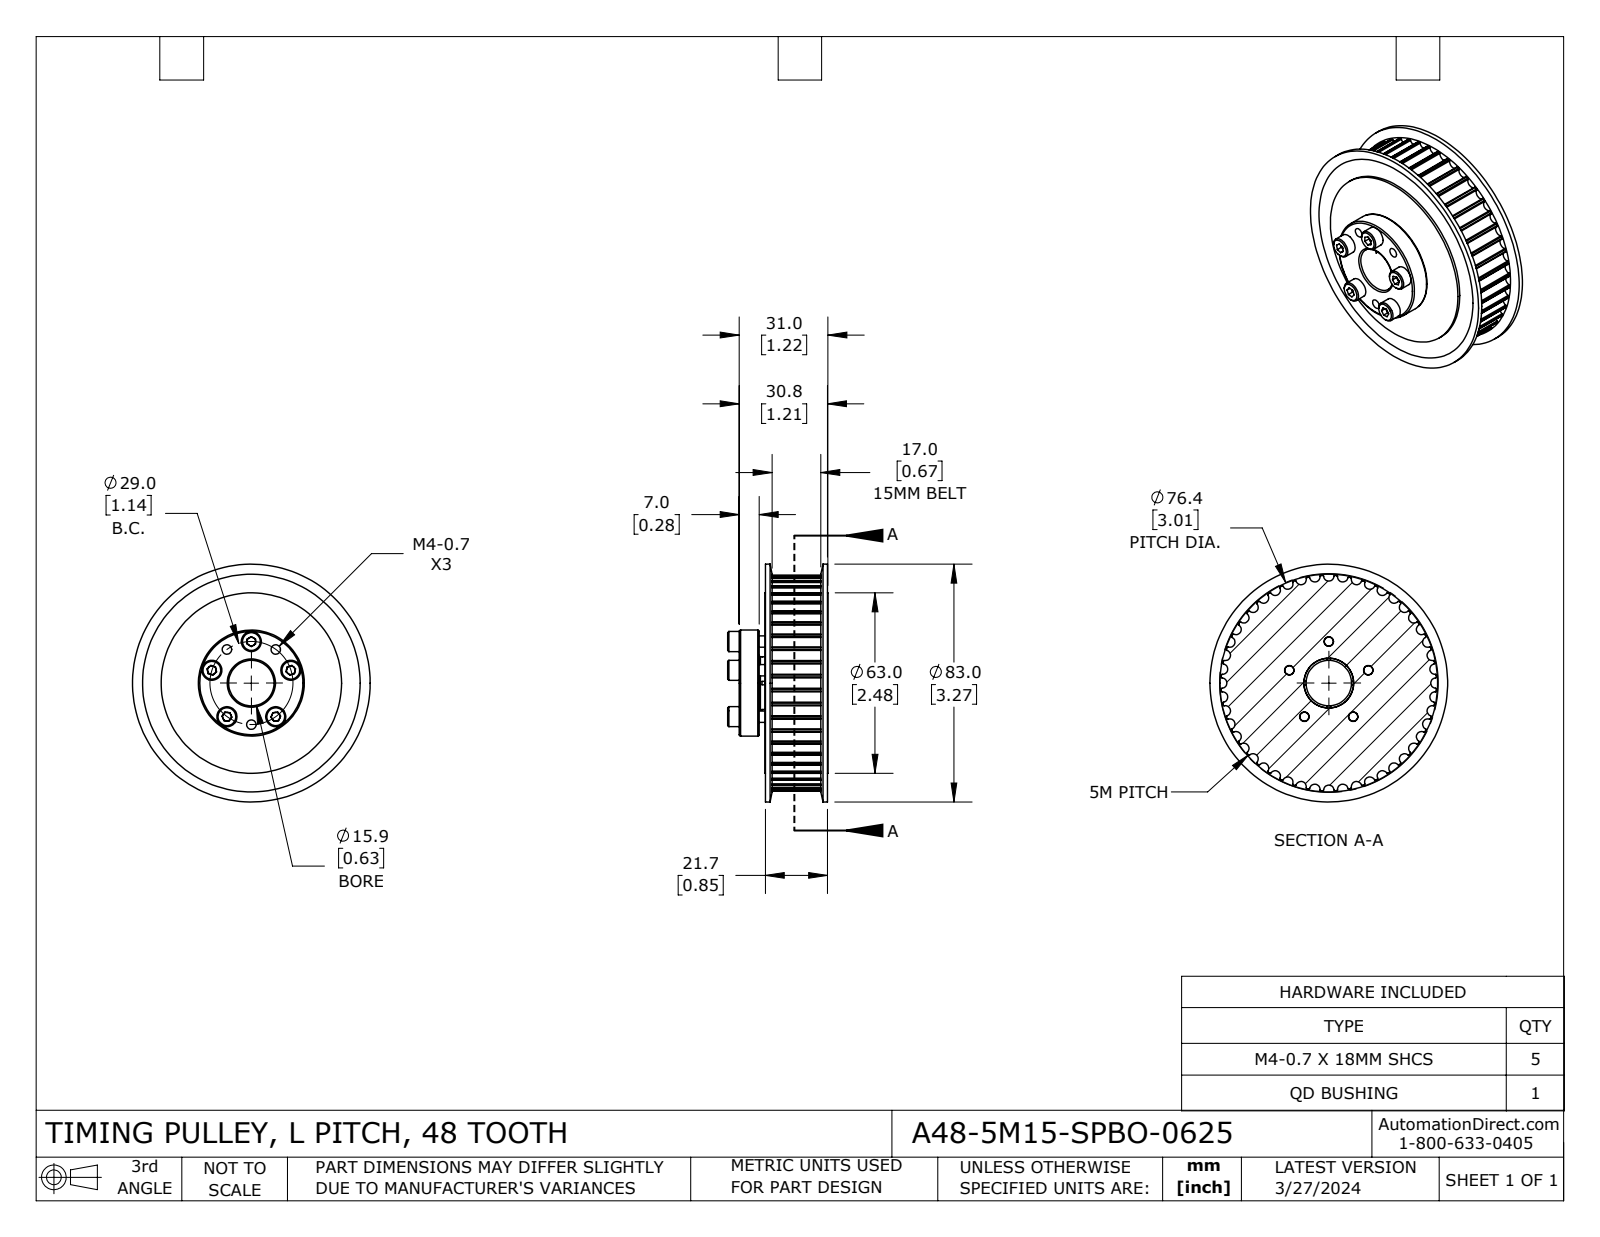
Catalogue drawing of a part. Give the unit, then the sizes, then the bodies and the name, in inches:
Units: inches
Overall size (bounding box): 3.268 × 3.268 × 1.378
Round holes (diameter × count): ⌀0.13 ×8, ⌀0.177 ×5, ⌀0.625 ×1, ⌀0.727 ×1, ⌀2.48 ×1
Round bosses / shafts (diameter × count): ⌀0.276 ×5, ⌀0.157 ×5, ⌀3.268 ×1, ⌀1.457 ×1
Partial cylindrical surfaces — rounded edges, fillets, slot ends (radius × count): R0.012 ×96, R0.072 ×48, R1.481 ×1
Main face-to-face distances: 0.098, 0.768, 0.035, 0.866, 0.831, 0.063, 0.732, 0.669, 0.795, 0.354
Hole centre spacings: 0.571, 1.086, 0.353, 0.924, 0.671, 1.142, 0.671
Volume: 5.854 in³ · Surface area: 53.1 in²
Bodies: 9 solids, 474 faces (101 planar, 307 cylindrical, 66 other)
Part name (STEP PRODUCT): A48-5M15-SPBO-0625
STEP written by: SolidWorks 2021 (CONFIG_CONTROL_DESIGN)
